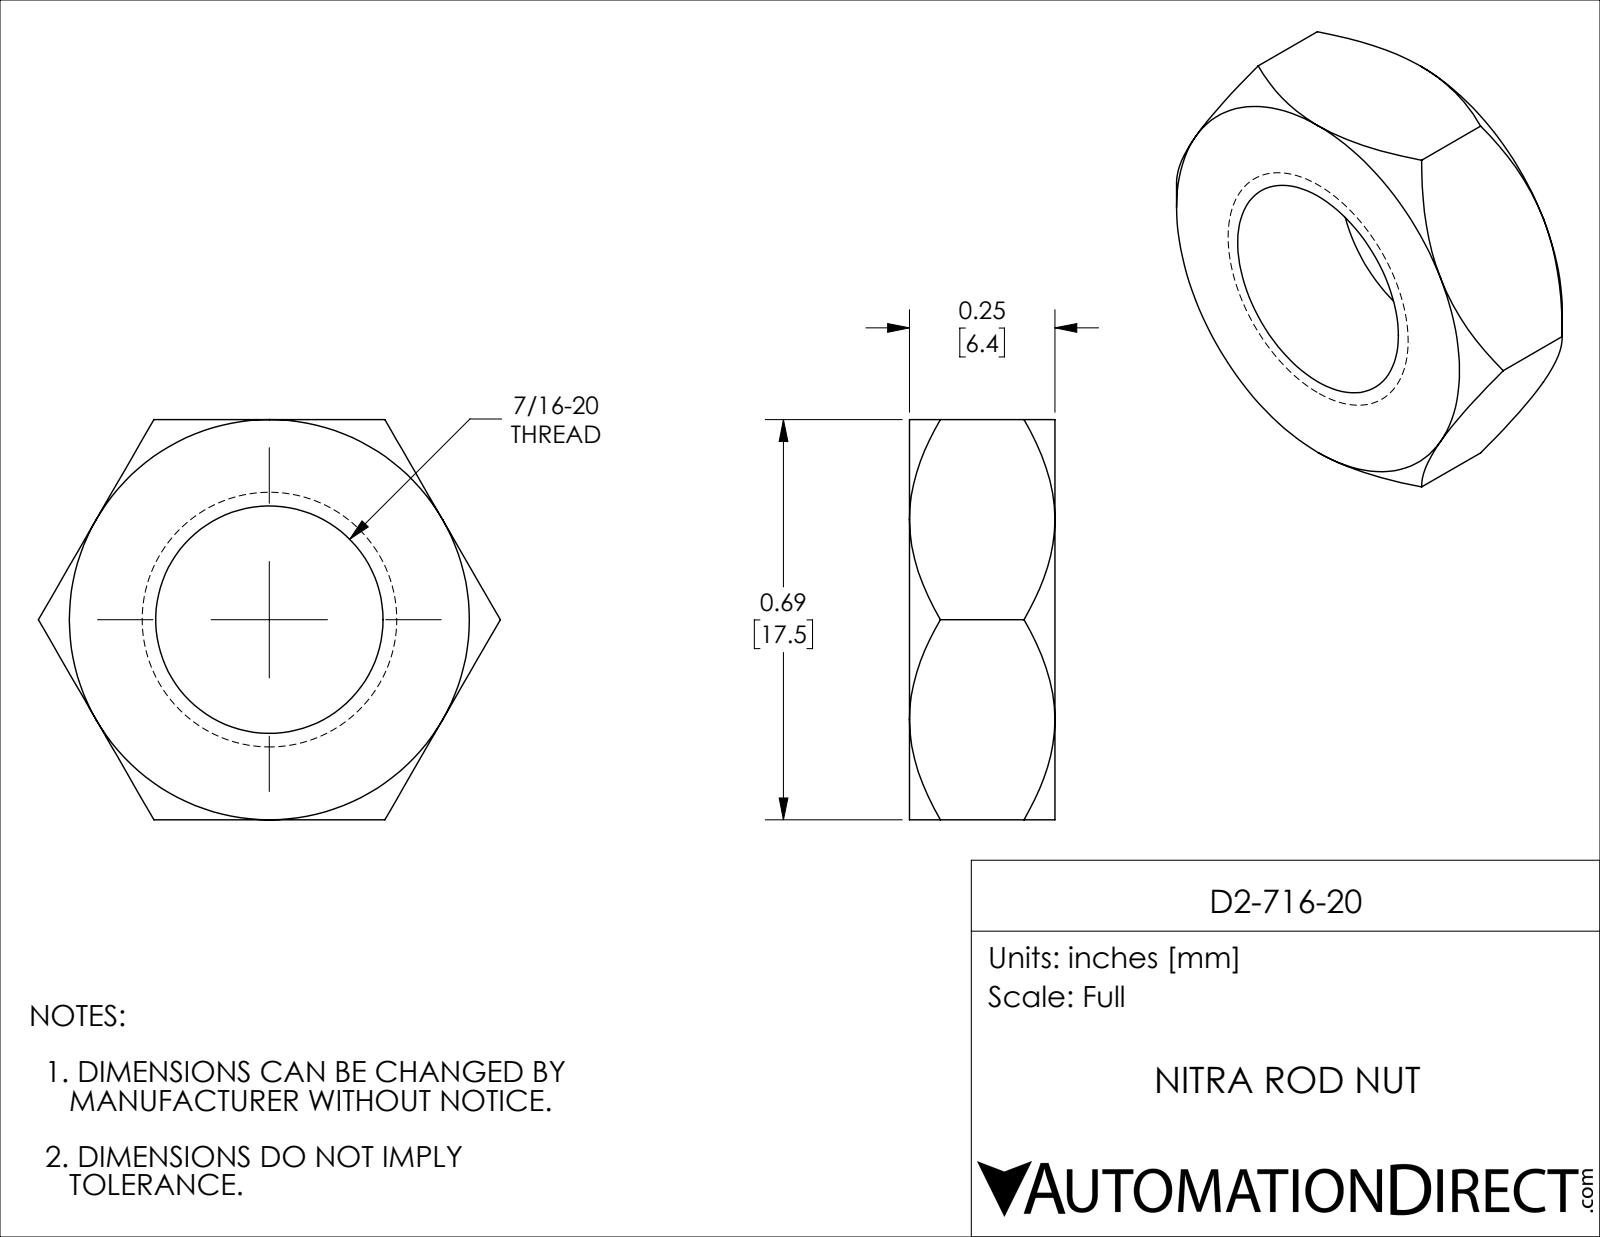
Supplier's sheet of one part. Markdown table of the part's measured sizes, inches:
| quantity | value |
| --- | --- |
| part name | D2-716-20 |
| STEP written by | SolidWorks 2019 (CONFIG_CONTROL_DESIGN) |
| units | inches |
| bodies | 1 solid, 24 faces (8 planar, 2 cylindrical, 14 other) |
| overall size | 0.794 × 0.688 × 0.25 |
| volume | 0.071 in³ |
| surface area | 1.426 in² |
| round holes (diameter × count) | 0.391 × 1 |
| main face-to-face distances | 0.687, 0.25 |
